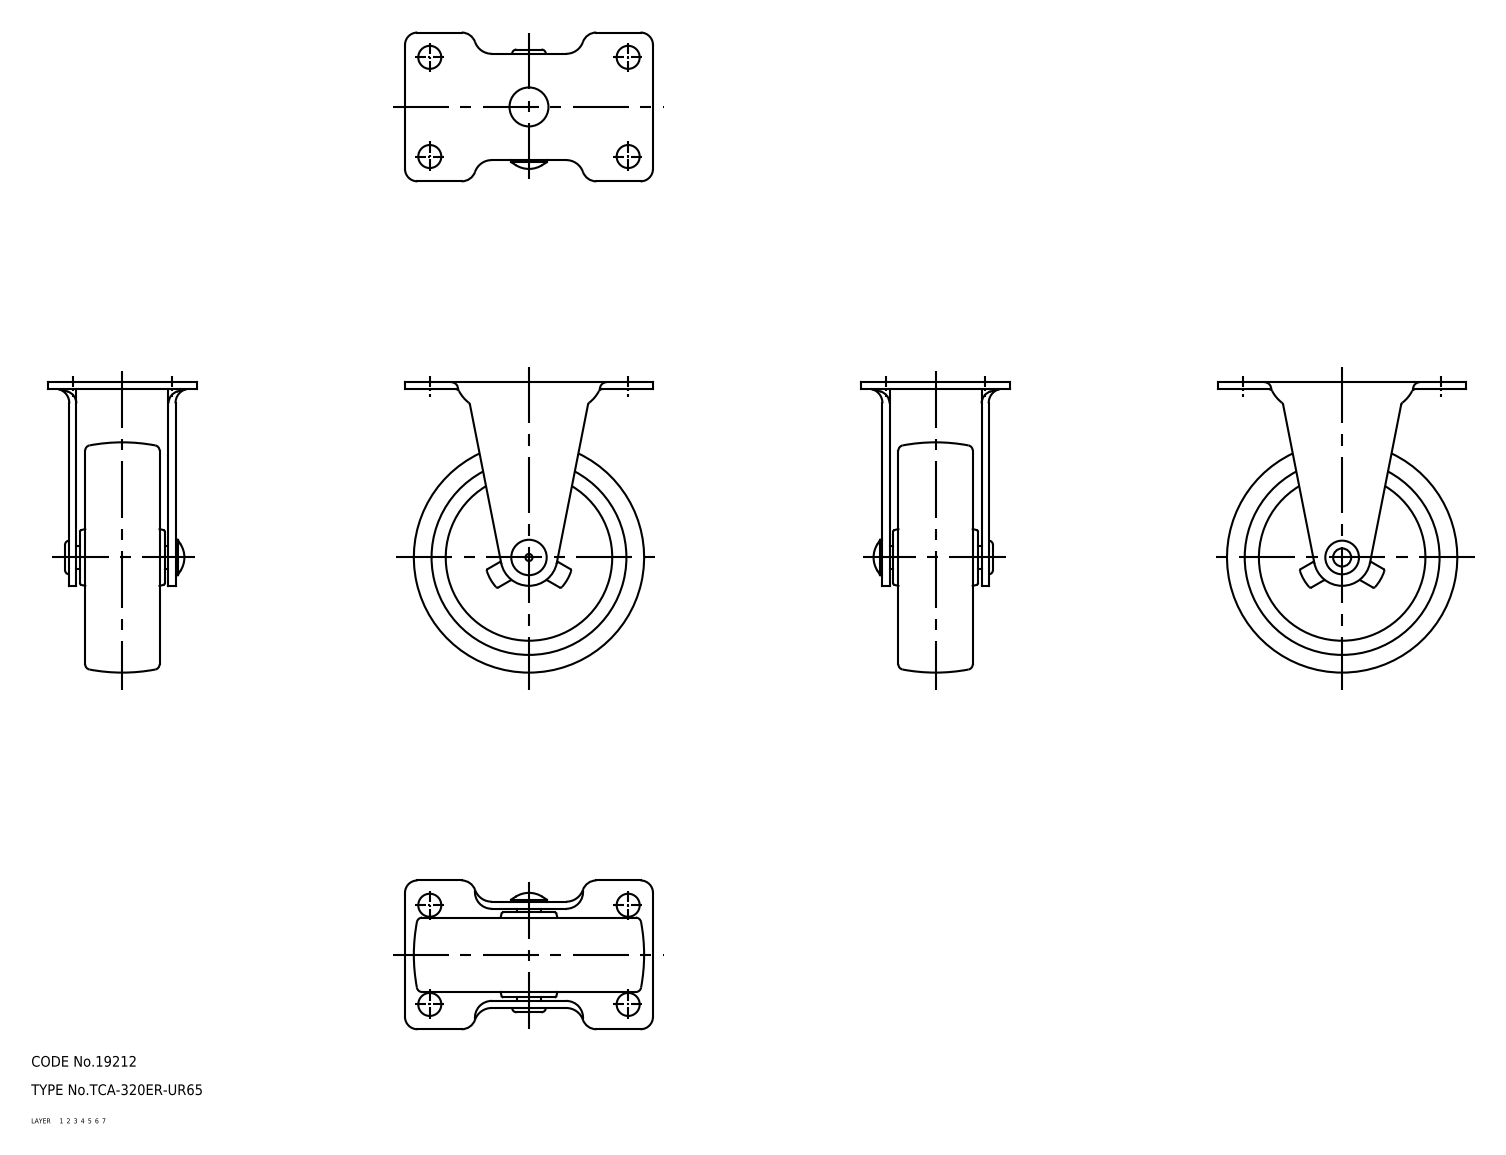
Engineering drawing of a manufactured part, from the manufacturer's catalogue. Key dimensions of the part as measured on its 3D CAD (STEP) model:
Part name (STEP PRODUCT): wheel; axle; 320ER_UR65_5423_36
STEP written by: CADfix (AUTOMOTIVE_DESIGN)
Units: millimetres
Bodies: 3 solids, 245 faces (0 planar, 0 cylindrical, 245 other)
Overall size (bounding box): 82 × 70 × 42
Volume: 63 875 mm³ · Surface area: 24 362 mm²
